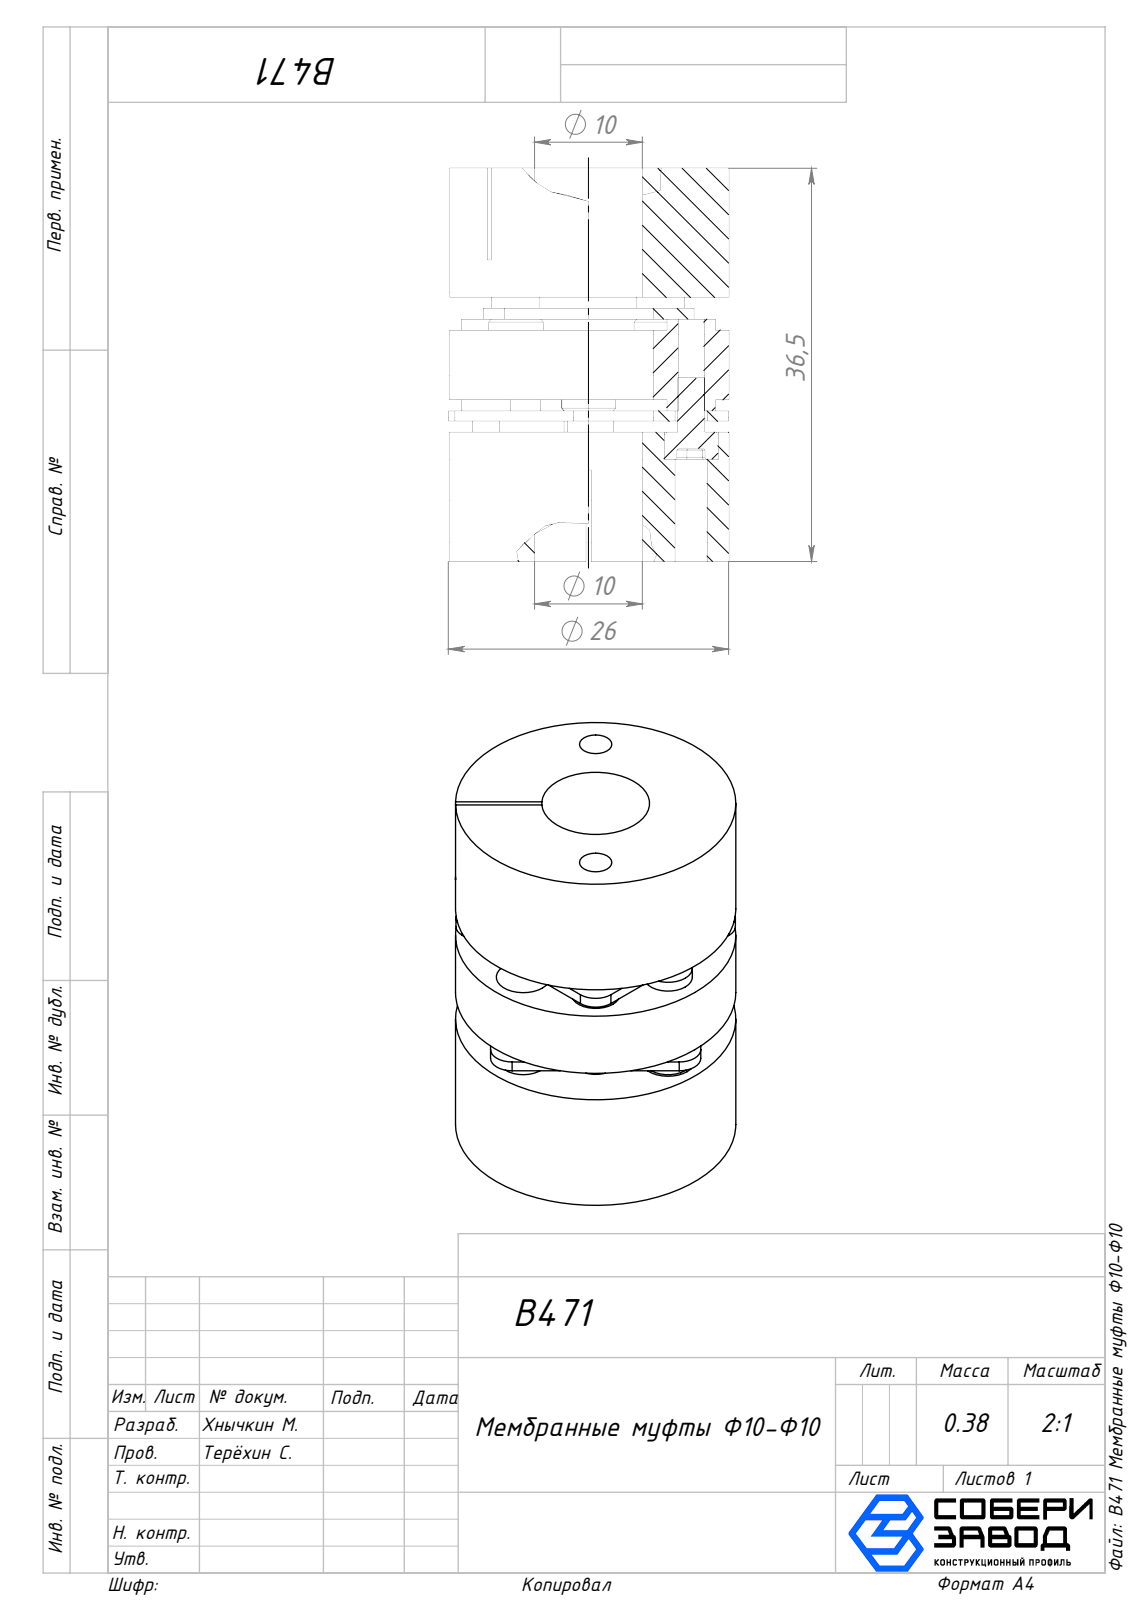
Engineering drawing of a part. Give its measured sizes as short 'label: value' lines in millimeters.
name: Винт_00; Верх_00; Средняя часть_00; Ниж.часть_00 (+1 more)
written by: SolidWorks 2025 (AUTOMOTIVE_DESIGN)
unit: mm
bodies: 11 solids, 362 faces (120 planar, 226 cylindrical, 16 other)
size: 36.5 × 26 × 26
volume: 13 480 mm³; area: 9 776 mm²
holes: 8× ⌀3, 8× ⌀5, 4× ⌀2.4, 1× ⌀10, 1× ⌀12
bosses: 8× ⌀4.5, 8× ⌀2.5, 1× ⌀26
rounds: 48× R0.1, 48× R0.25, 8× R2
face distances: 1, 9.5, 2, 12, 10.5, 24.5, 14, 8.5, 15, 3
hole spacings: 7.27, 9.5, 13.44, 17.56, 19, 19.01
